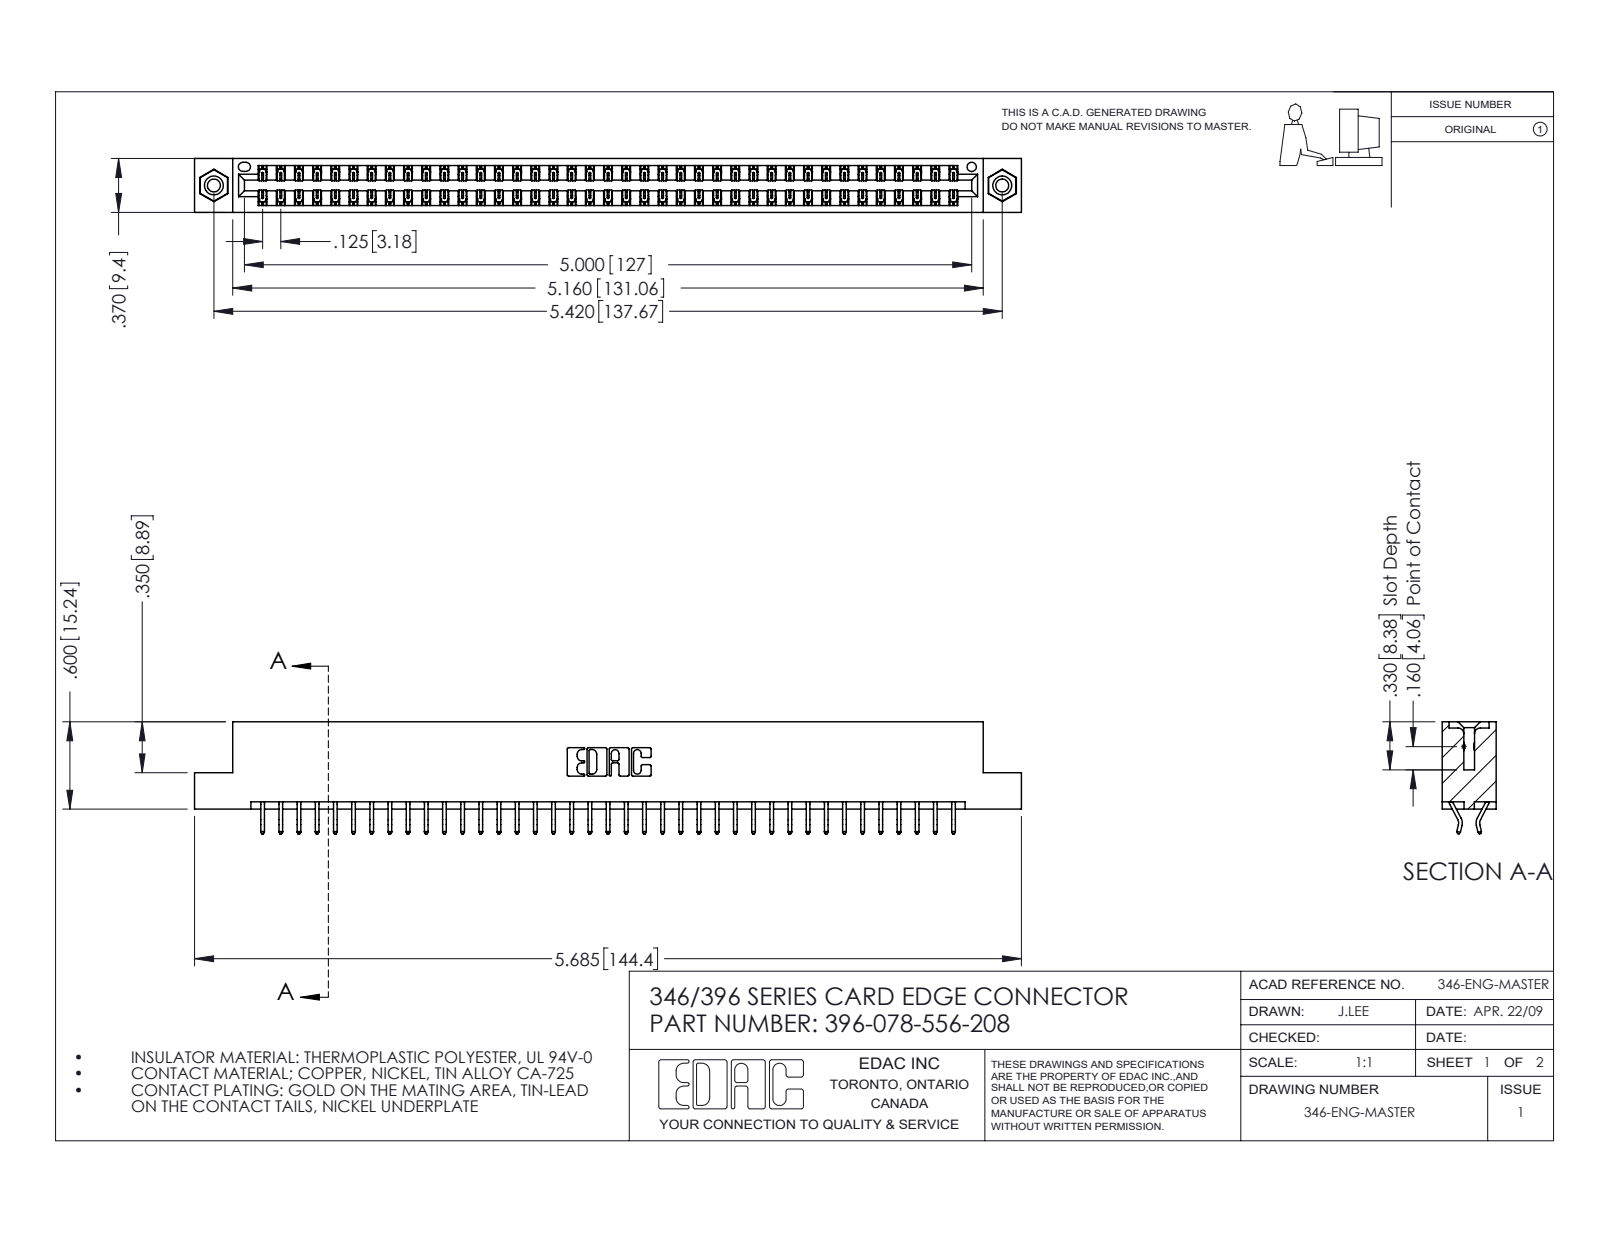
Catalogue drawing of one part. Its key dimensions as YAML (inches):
part_name: "396-078-556-208; 346 Part_Flush Mounting Lugs - 0.156 Dia-TI; 345-292-001_556 Tail; 345-250-001_345-250-003-102"
step_written_by: "SolidWorks 2016 (CONFIG_CONTROL_DESIGN)"
units: inches
bodies: {solids: 81, faces: 4706, planar: 3150, cylindrical: 1540, other: 16}
overall_size: [5.685, 0.77, 0.37]
volume: 0.857
surface_area: 29.78
round_holes:
  - {diameter: 0.089, count: 2}
  - {diameter: 0.125, count: 2}
  - {diameter: 0.156, count: 2}
  - {diameter: 0.064, count: 1}
round_bosses_or_shafts:
  - {diameter: 0.155, count: 2}
partial_cylinders:
  - {radius: 0.006, count: 117}
  - {radius: 0.01, count: 22}
  - {radius: 0.007, count: 6}
  - {radius: 0.031, count: 6}
  - {radius: 0.026, count: 3}
  - {radius: 0.01, count: 2}
  - {radius: 0.014, count: 2}
  - {radius: 0.022, count: 2}
face_to_face_distances: [0.048, 0.322, 0.37, 0.25, 0.025, 0.072, 0.298, 0.275, 0.148, 0.222]
hole_center_spacings: [0.246, 5.211, 5.42]
